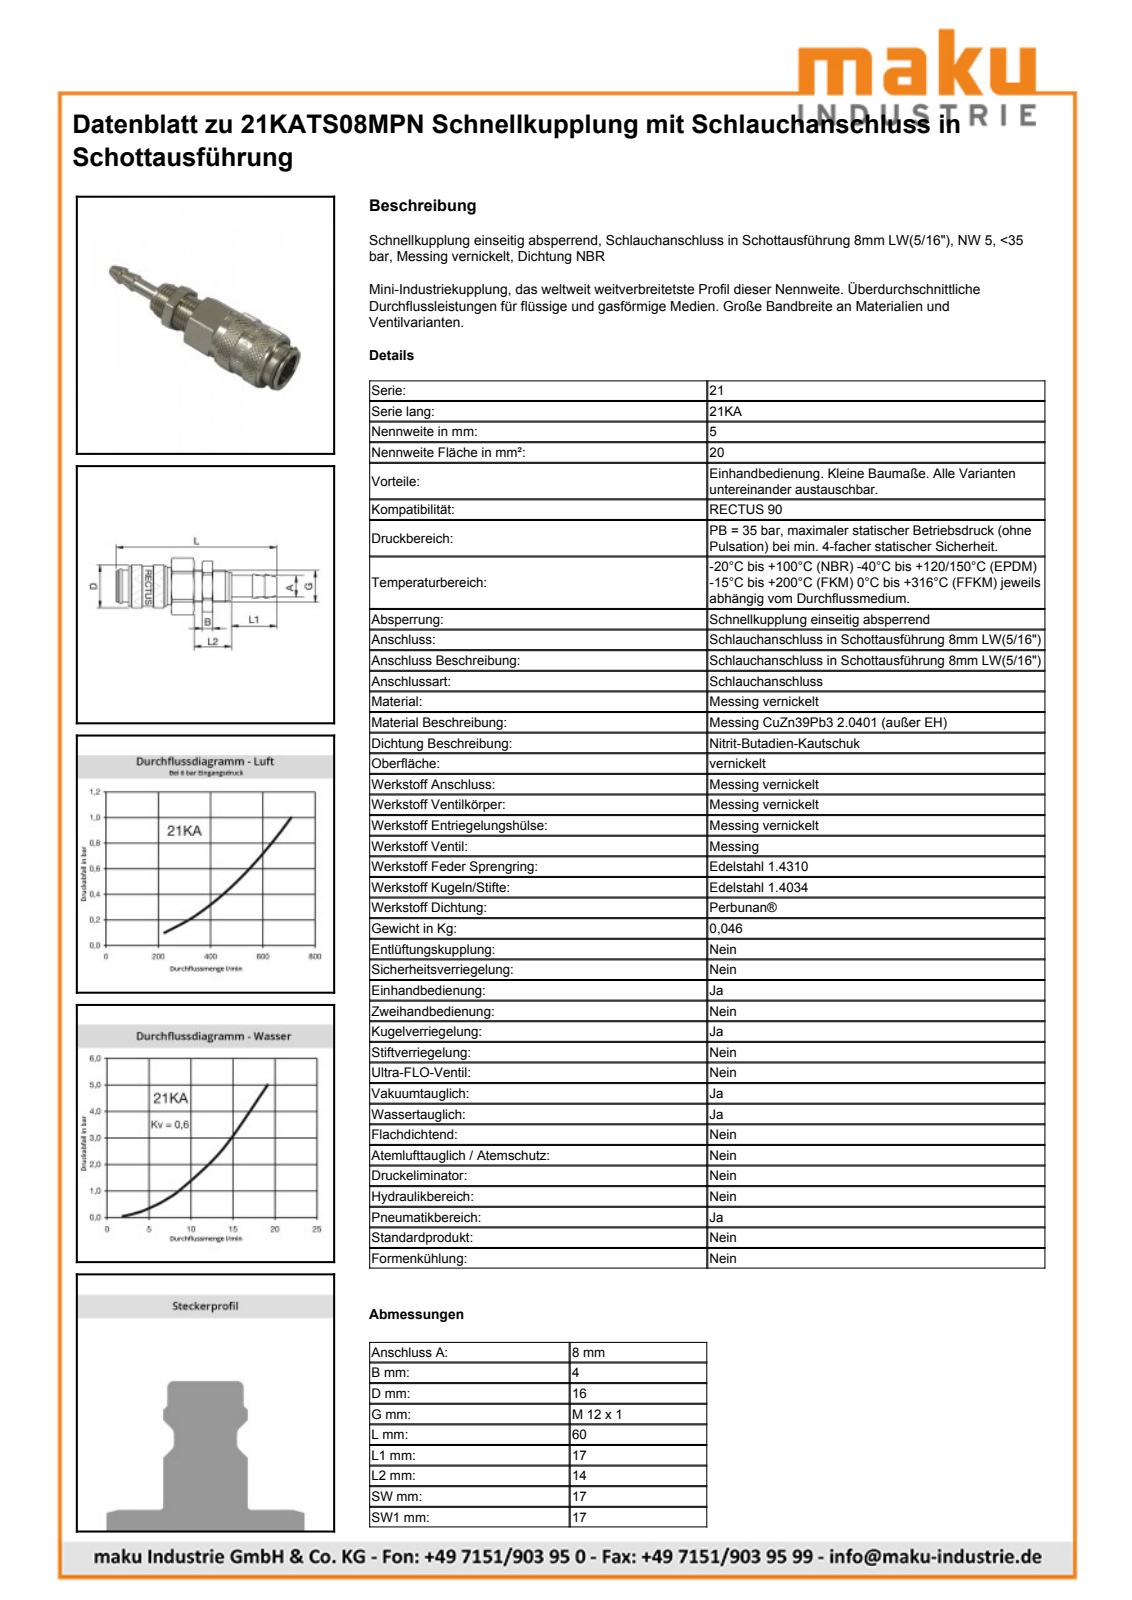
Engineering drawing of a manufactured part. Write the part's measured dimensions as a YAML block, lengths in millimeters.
part_name: "D104304"
step_written_by: "Autodesk Inventor 2011 (AUTOMOTIVE_DESIGN)"
units: millimeters
bodies: {solids: 2, faces: 531, planar: 208, cylindrical: 70, other: 253}
overall_size: [60.15, 19.09, 18.21]
volume: 8328
surface_area: 4767
round_holes:
  - {diameter: 12.15, count: 1}
  - {diameter: 14, count: 1}
round_bosses_or_shafts:
  - {diameter: 16.15, count: 1}
  - {diameter: 15.1, count: 1}
  - {diameter: 12, count: 1}
  - {diameter: 11.4, count: 1}
  - {diameter: 11.24, count: 1}
  - {diameter: 11.15, count: 1}
  - {diameter: 10.6, count: 1}
  - {diameter: 8.05, count: 1}
partial_cylinders:
  - {radius: 7.45, count: 1}
  - {radius: 9.57, count: 1}
face_to_face_distances: [17, 29.15, 37.33, 8.18, 33.33, 4.18, 4, 20.6, 8.55, 12.73]
